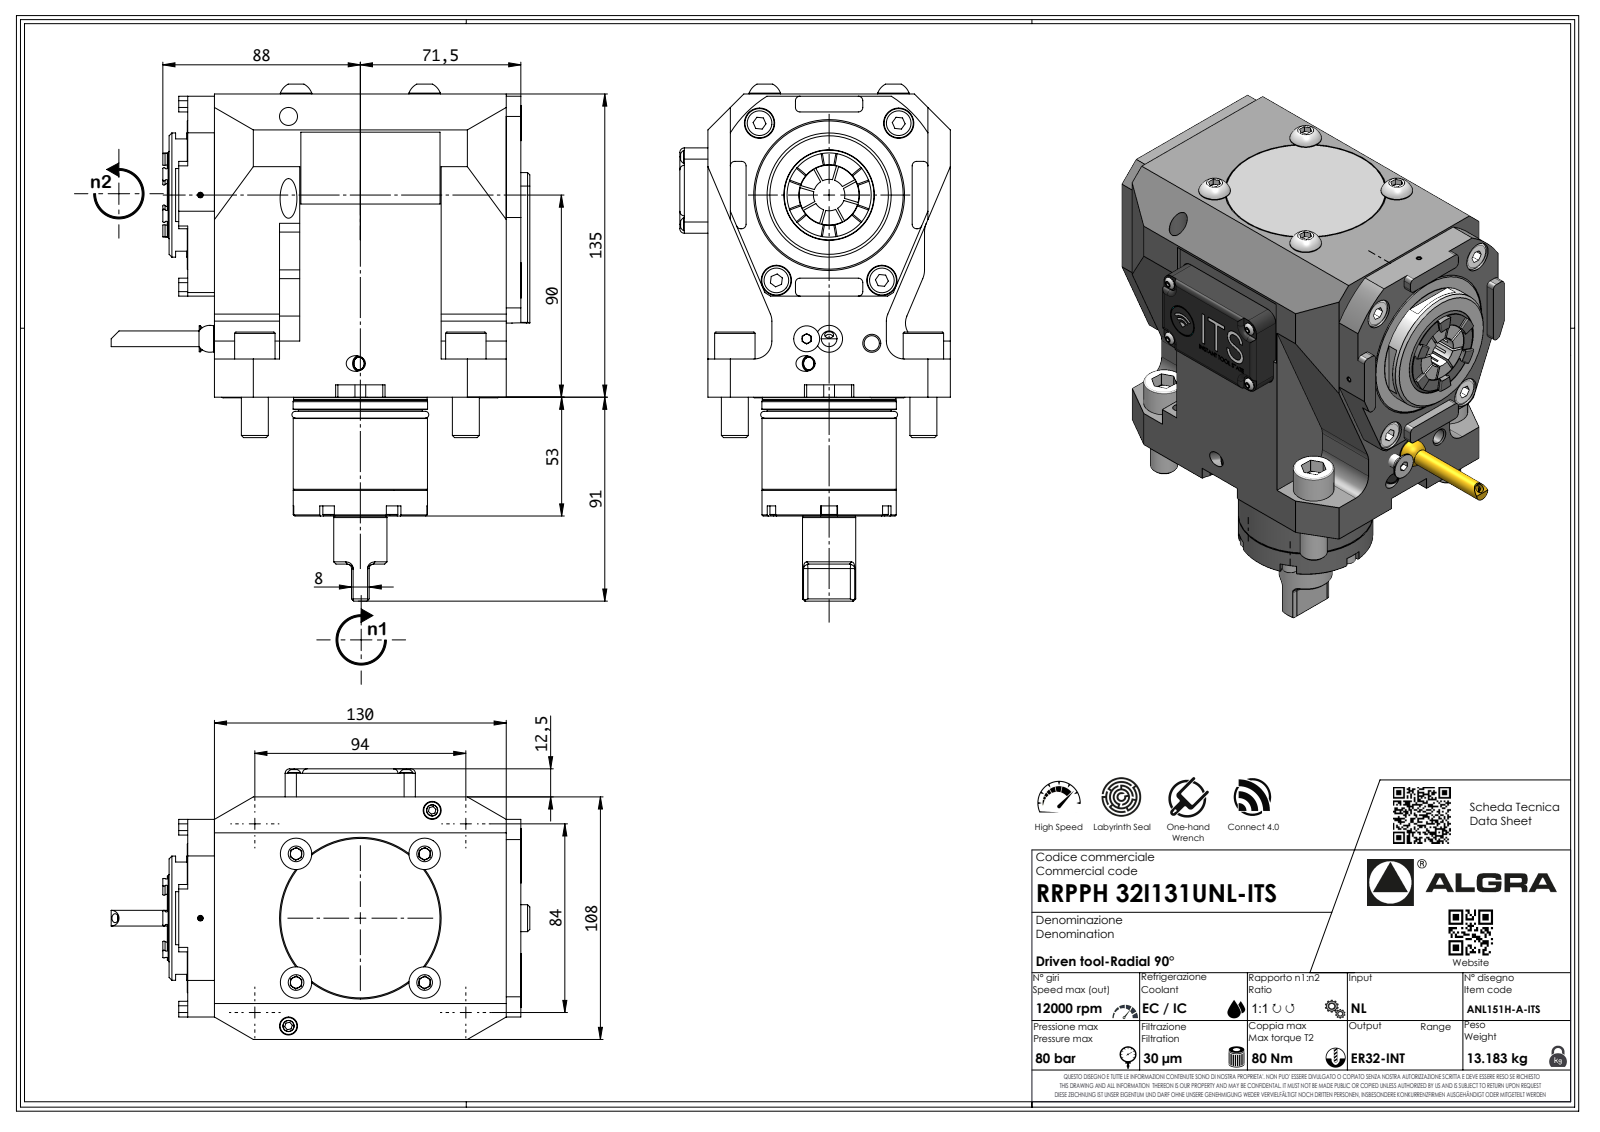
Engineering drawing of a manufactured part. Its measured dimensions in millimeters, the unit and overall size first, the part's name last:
Units: millimetres
Overall size (bounding box): 225.8 × 163.48 × 122
Round holes (diameter × count): ⌀2.1 ×1
Round bosses / shafts (diameter × count): ⌀60 ×1, ⌀55.3 ×1, ⌀37.5 ×1, ⌀23.7 ×1, ⌀6.37 ×1, ⌀1.7 ×1
Partial cylindrical surfaces — rounded edges, fillets, slot ends (radius × count): R2 ×22, R8 ×22, R5 ×12, R0.33 ×7, R0.52 ×7, R3.7 ×7, R3.75 ×4, R6 ×4
Main face-to-face distances: 135, 108, 29, 101, 17, 136.5, 12, 6.5, 11.5, 148.5
Volume: 1 997 000 mm³ · Surface area: 119 385 mm²
Bodies: 1 solid, 634 faces (403 planar, 108 cylindrical, 123 other)
Part name (STEP PRODUCT): RRPPH32I131UNL-ITS
STEP written by: SolidWorks 2023 (AUTOMOTIVE_DESIGN)
